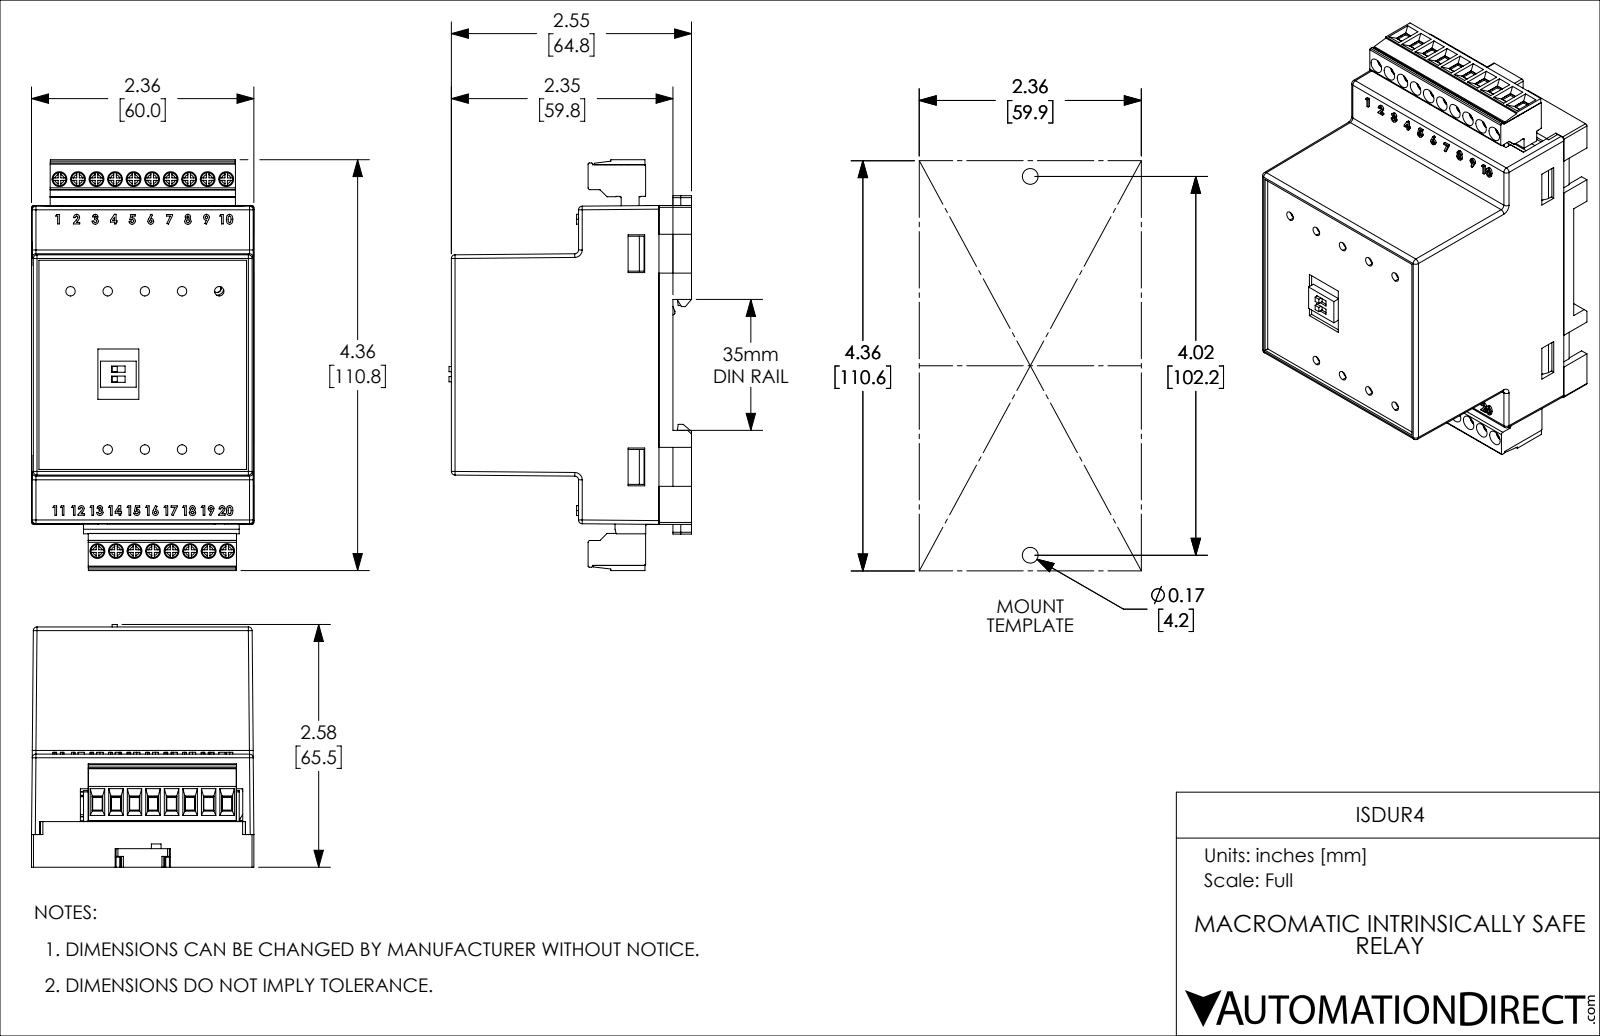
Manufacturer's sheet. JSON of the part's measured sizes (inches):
{"part_name": "ISDUR4", "step_written_by": "SolidWorks 2019 (AUTOMOTIVE_DESIGN)", "units": "inches", "bodies": {"solids": 26, "faces": 1877, "planar": 1274, "cylindrical": 335, "other": 268}, "overall_size": [4.362, 2.577, 2.362], "volume_in3": 3.634, "surface_area_in2": 108, "round_holes": [[0.157, 18], [0.1, 9]], "round_bosses_or_shafts": [[0.138, 18], [0.148, 2], [0.091, 2], [0.087, 2]], "partial_cylinders_radius": [[0.02, 66], [0.01, 64], [0.039, 18], [0.021, 16], [0.02, 8], [0.012, 6], [0.006, 5], [0.03, 4]], "face_to_face_distances": [0.059, 0.094, 2.256, 2.161, 2.315, 2.22, 1.311, 0.85, 0.197, 0.291], "hole_center_spacings": [0.197, 0.394, 0.591, 0.787, 0.984, 3.949, 3.954, 3.969]}
